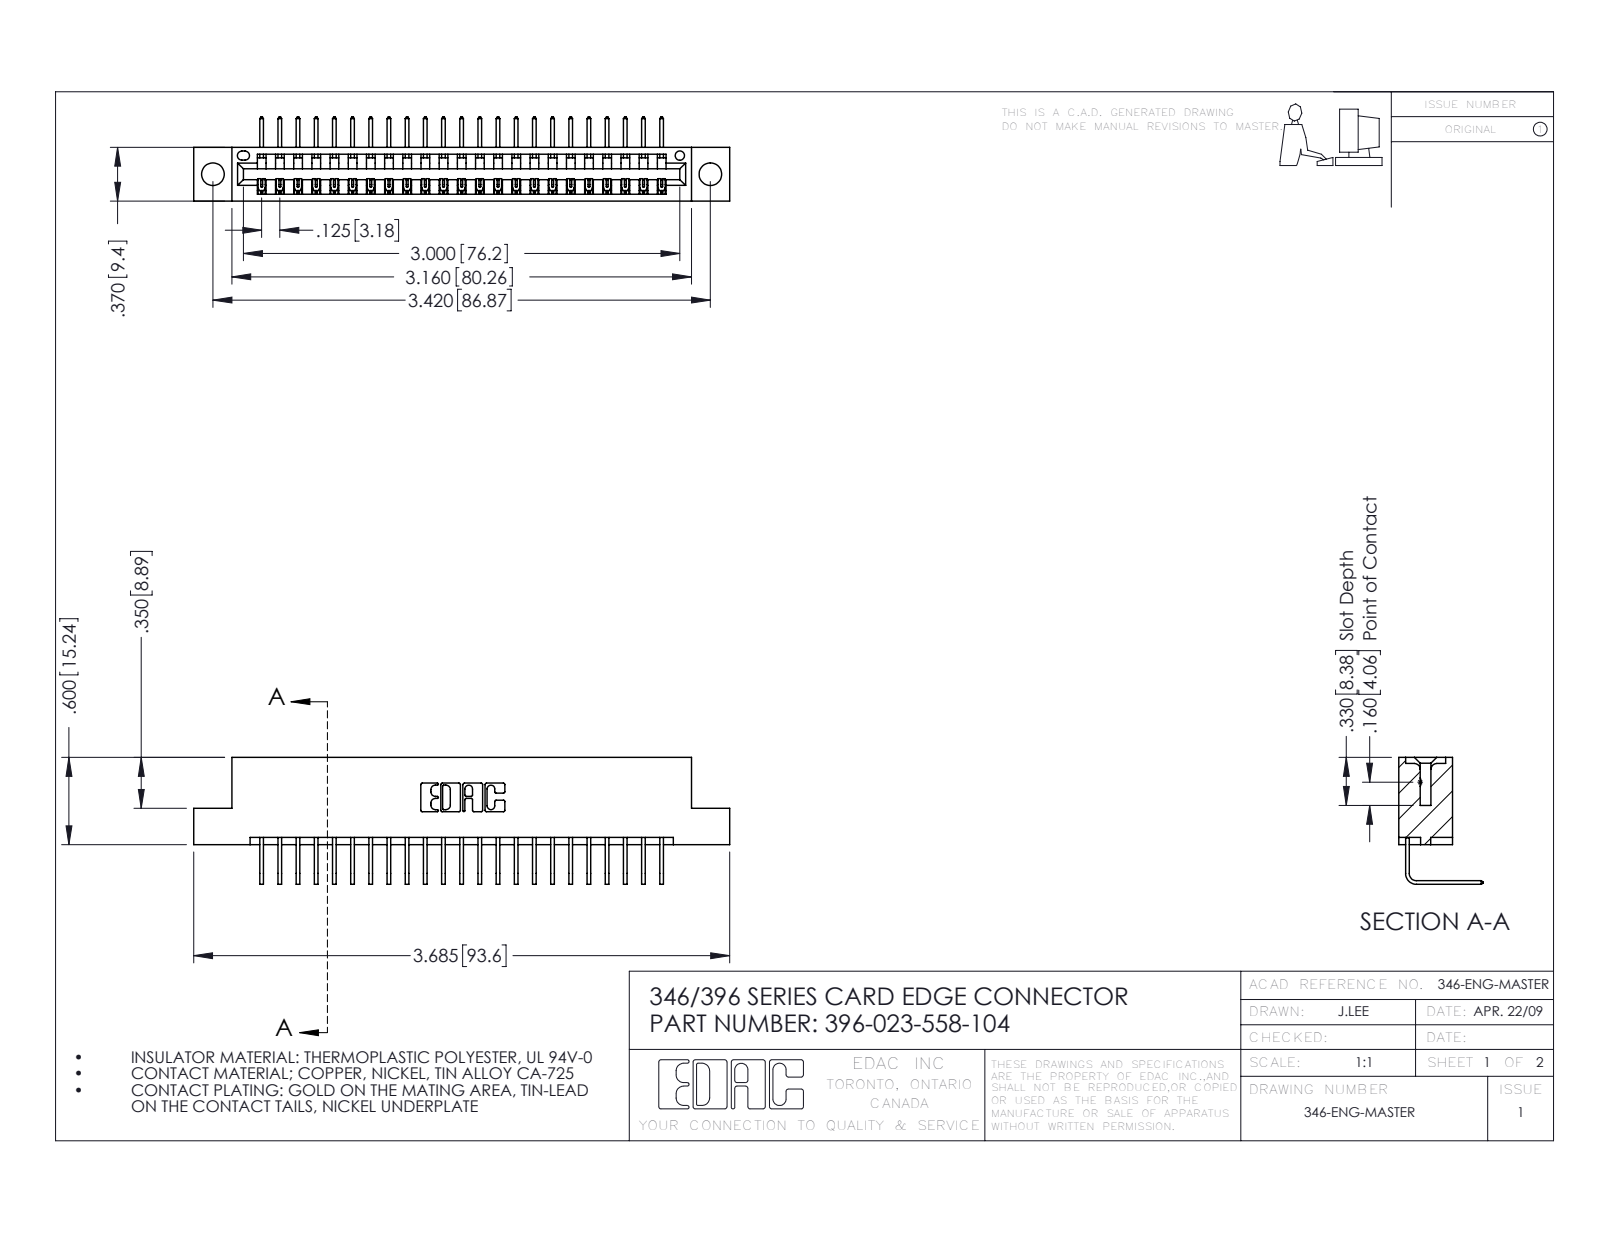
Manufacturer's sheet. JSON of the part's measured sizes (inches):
{"part_name": "346 Part_Flush Mounting Lugs - 0.156 Dia-TH; 396-023-558-104; 345-292-001_558 Tail - 2", "step_written_by": "SolidWorks 2016 (CONFIG_CONTROL_DESIGN)", "units": "inches", "bodies": {"solids": 24, "faces": 1502, "planar": 1042, "cylindrical": 460, "other": 0}, "overall_size": [3.685, 0.873, 0.58], "volume_in3": 0.538, "surface_area_in2": 17.17, "round_holes": [[0.156, 2], [0.064, 1]], "partial_cylinders_radius": [[0.006, 46], [0.01, 22], [0.007, 6], [0.031, 6], [0.026, 3], [0.031, 2], [0.04, 2], [0.014, 1]], "face_to_face_distances": [0.322, 0.048, 0.25, 0.37, 0.298, 0.025, 0.072, 0.148, 0.222, 0.1], "hole_center_spacings": [0.246, 3.212, 3.42]}
